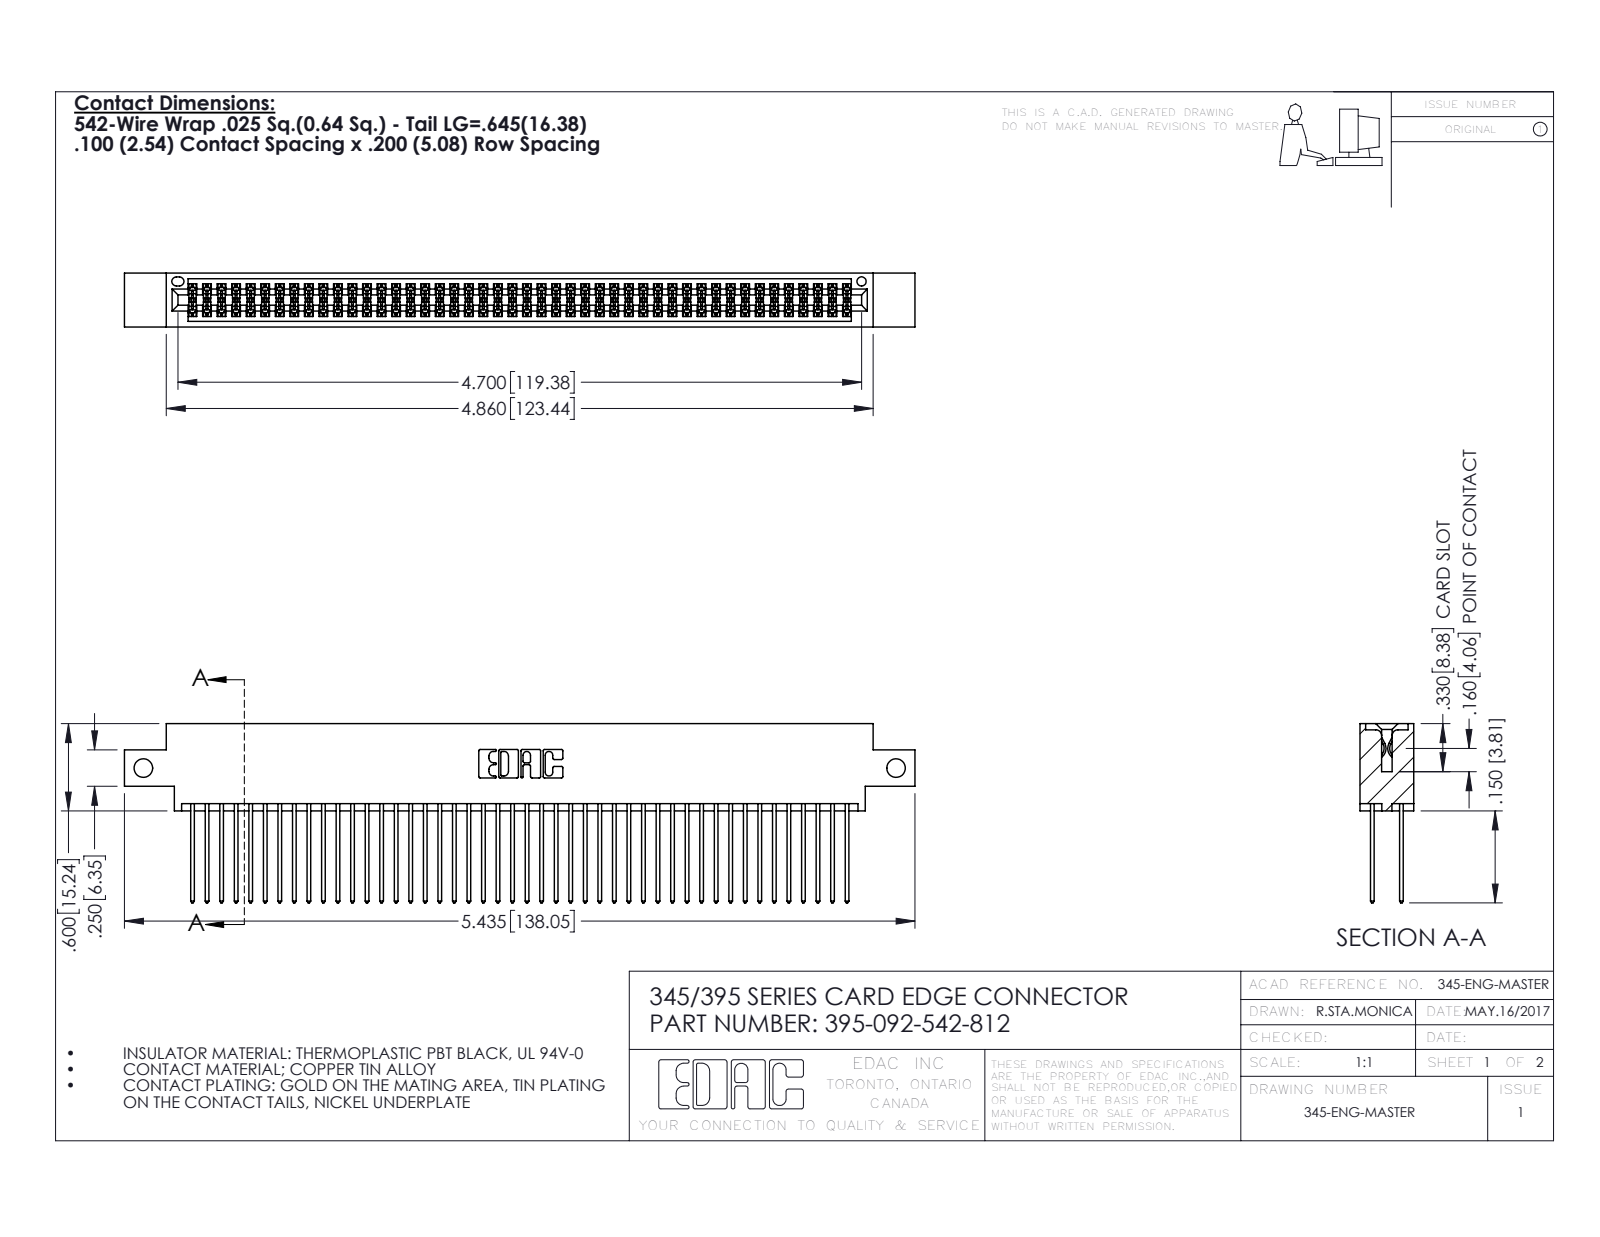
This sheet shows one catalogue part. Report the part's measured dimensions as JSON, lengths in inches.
{"part_name": "345-292-001_345-293-142; 345 Part_0.170 Offset - Side Mount; 395-092-542-812", "step_written_by": "SolidWorks 2016 (CONFIG_CONTROL_DESIGN)", "units": "inches", "bodies": {"solids": 93, "faces": 4730, "planar": 3120, "cylindrical": 1610, "other": 0}, "overall_size": [5.435, 1.232, 0.37], "volume_in3": 0.835, "surface_area_in2": 34.57, "round_holes": [[0.128, 2], [0.064, 1]], "partial_cylinders_radius": [[0.006, 138], [0.01, 92], [0.01, 22], [0.007, 6], [0.031, 6], [0.026, 3], [0.014, 2], [0.019, 2]], "face_to_face_distances": [0.298, 0.072, 0.2, 0.098, 0.272, 0.025, 0.37, 0.225, 0.175, 0.149], "hole_center_spacings": [5.175]}
